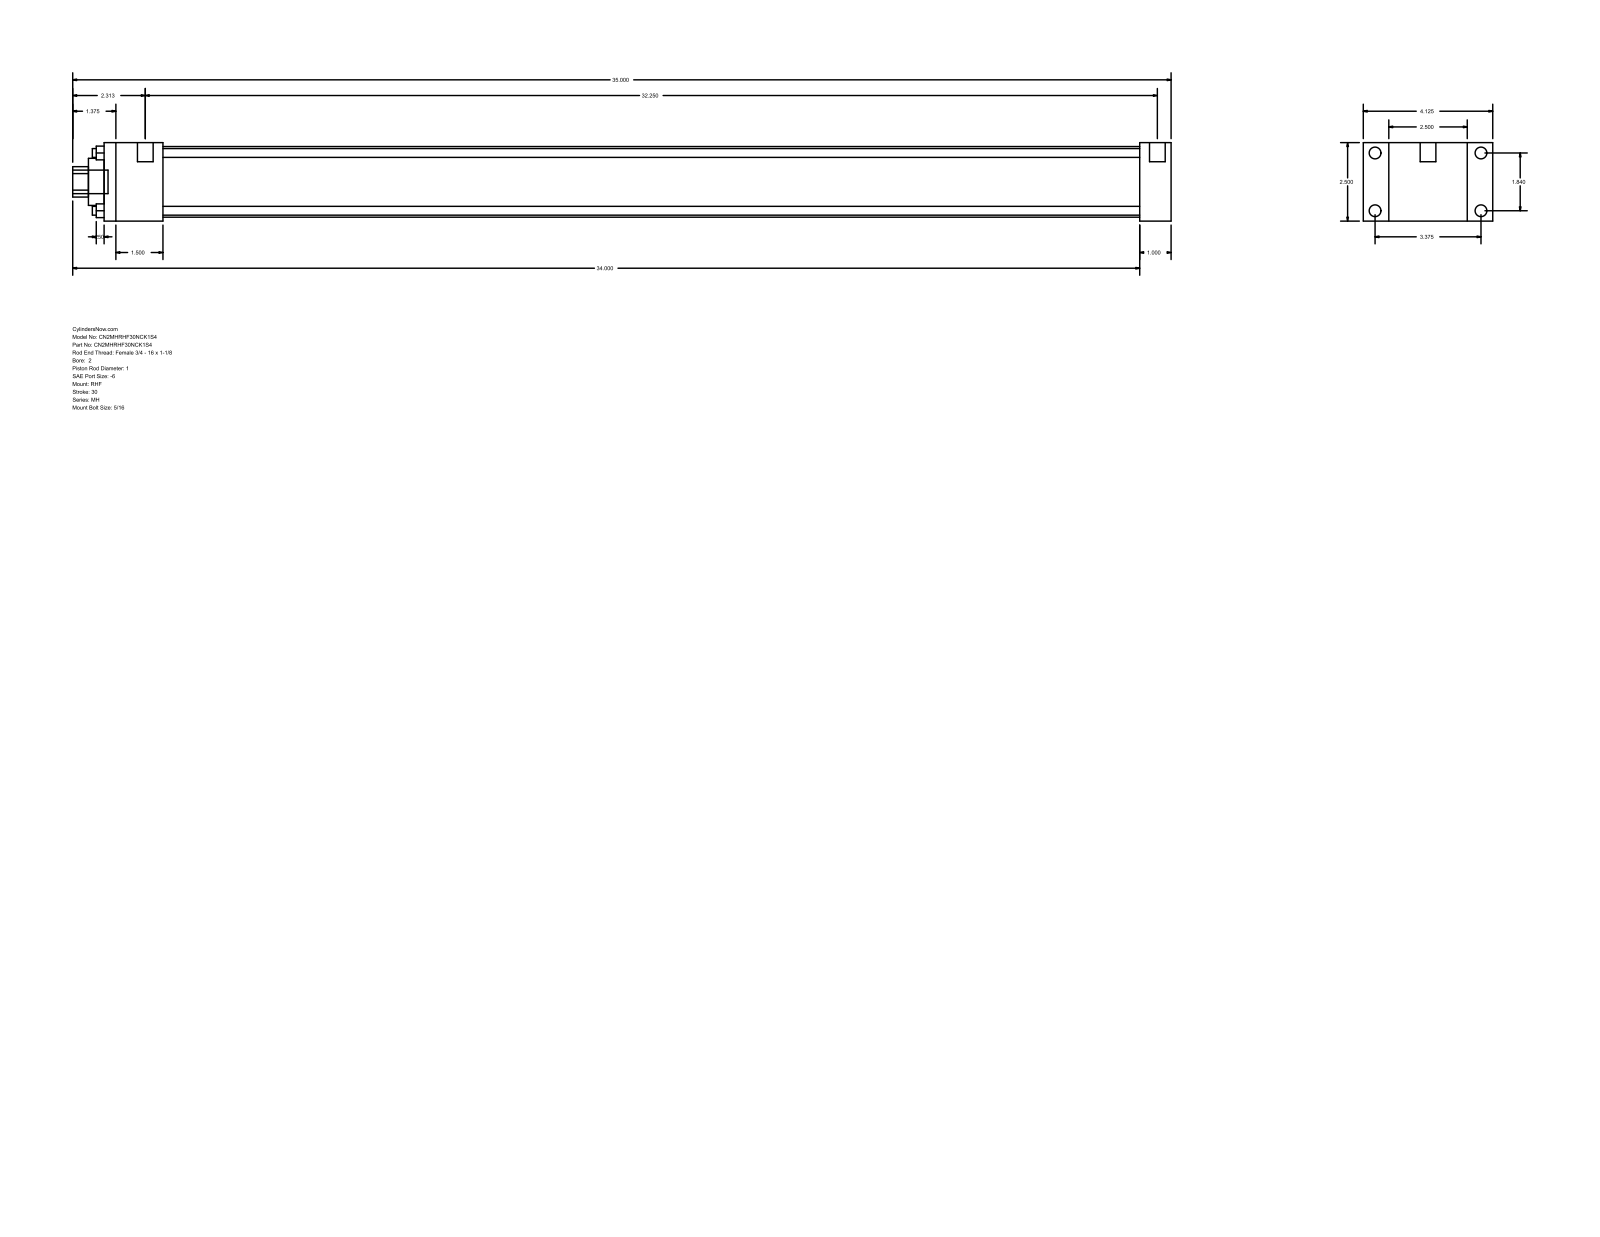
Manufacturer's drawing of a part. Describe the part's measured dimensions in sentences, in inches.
The part is named "MH_RHF__0200_1". Its 3-D file was written by "GSSL Pune (CONFIG_CONTROL_DESIGN)". It is 0 solids with 88 faces: 60 planar, 28 cylindrical and 0 other. Overall it measures 35 by 4.125 by 2.5 inches. Round holes: 4 of diameter 0.281, 1 of diameter 1, 1 of diameter 1.5, 1 of diameter 2.25. Round bosses or shafts: 4 of diameter 0.375, 4 of diameter 0.219, 2 of diameter 0.5, 1 of diameter 0.75. Partial cylindrical surfaces (rounded edges, fillets, slot ends): 1 of radius 0.484. The main face-to-face distances are 2.5, 1, 0.813, 3.313, 34, 33, 4.125, 1.875, 31.125, 32.125. The hole center spacings are 1.301, 1.84, 2.602.
